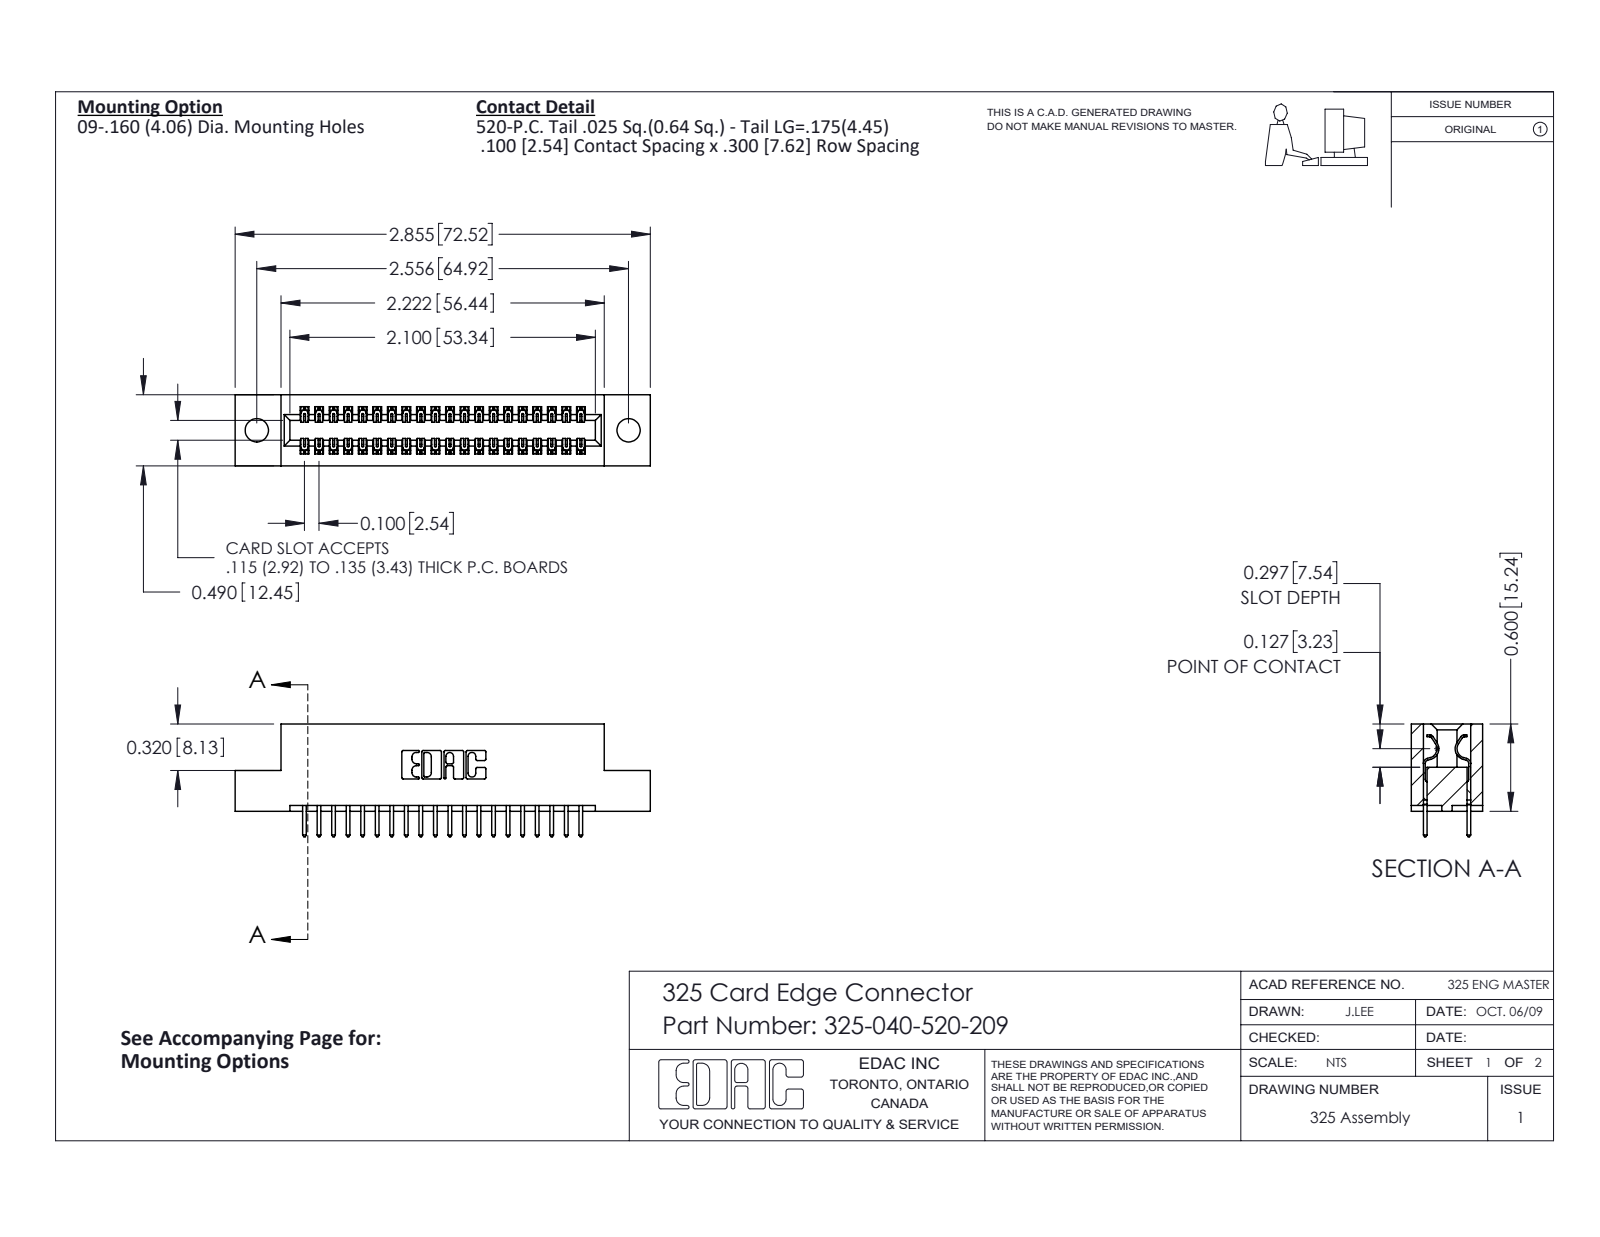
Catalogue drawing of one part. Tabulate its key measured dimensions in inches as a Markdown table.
| quantity | value |
| --- | --- |
| part name | 325-292-001_325-293-120; 325 Part_.160 TH; 325-040-520-209 |
| STEP written by | SolidWorks 2016 (CONFIG_CONTROL_DESIGN) |
| units | inches |
| bodies | 41 solids, 2194 faces (1510 planar, 684 cylindrical, 0 other) |
| overall size | 2.855 × 0.775 × 0.49 |
| volume | 0.545 in³ |
| surface area | 15.69 in² |
| round holes (diameter × count) | 0.16 × 2 |
| partial cylindrical surfaces (radius × count) | 0.006 × 60, 0.01 × 40, 0.01 × 22, 0.007 × 6, 0.031 × 6, 0.026 × 3, 0.014 × 2, 0.022 × 2 |
| main face-to-face distances | 0.083, 0.407, 0.3, 0.49, 0.107, 0.383, 0.025, 0.325, 0.04, 0.1 |
| hole center spacings | 2.556 |
